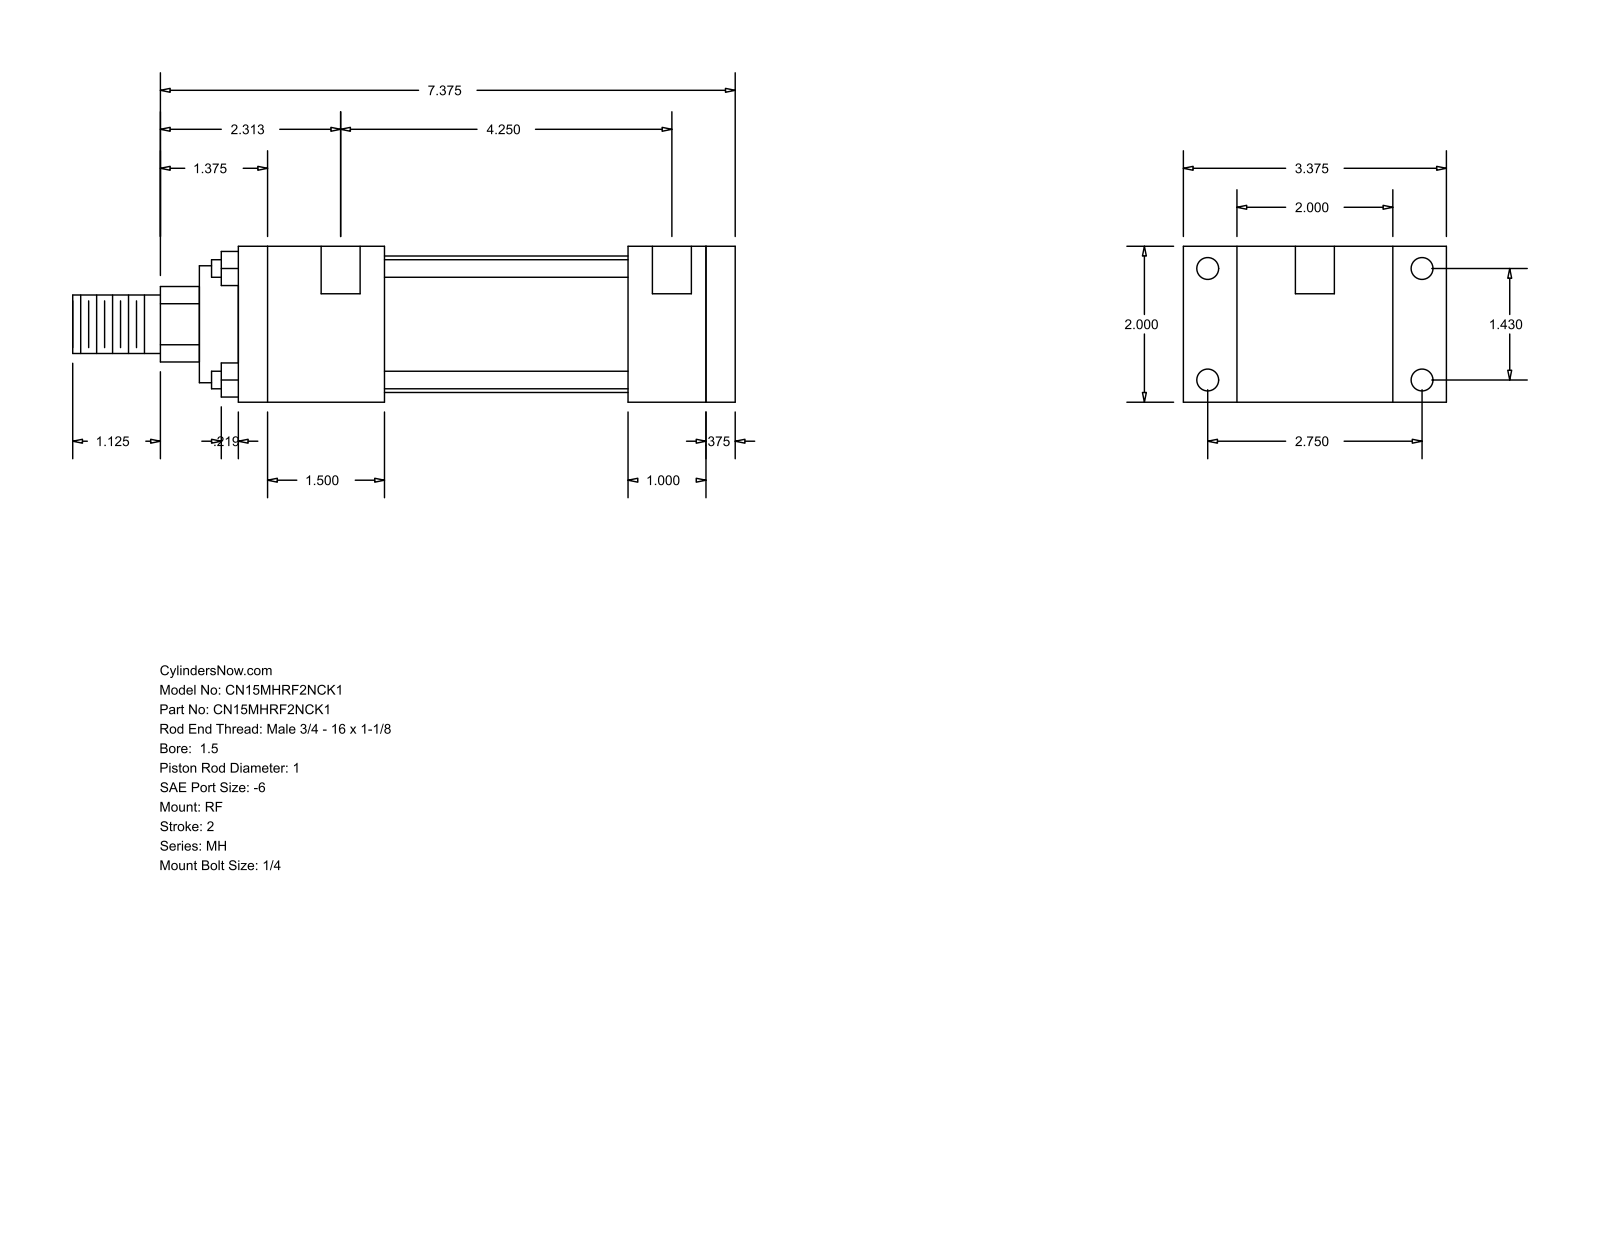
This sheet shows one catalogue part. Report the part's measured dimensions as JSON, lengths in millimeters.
{"part_name": "MH_RF__0150_1", "step_written_by": "GSSL Pune (CONFIG_CONTROL_DESIGN)", "units": "millimeters", "bodies": {"solids": 0, "faces": 92, "planar": 64, "cylindrical": 28, "other": 0}, "overall_size": [215.9, 85.72, 50.8], "round_holes": [[5.56, 4], [7.14, 4], [12.7, 2]], "round_bosses_or_shafts": [[5.71, 4], [44.45, 1], [38.1, 1], [25.4, 1], [19.05, 1]], "partial_cylinders_radius": [[12.29, 1]], "face_to_face_distances": [50.8, 9.52, 152.4, 25.4, 161.92, 17.46, 68.26, 127, 34.92, 47.63], "hole_center_spacings": [36.32, 69.84, 78.72, 111.13, 3.18, 107.95]}
